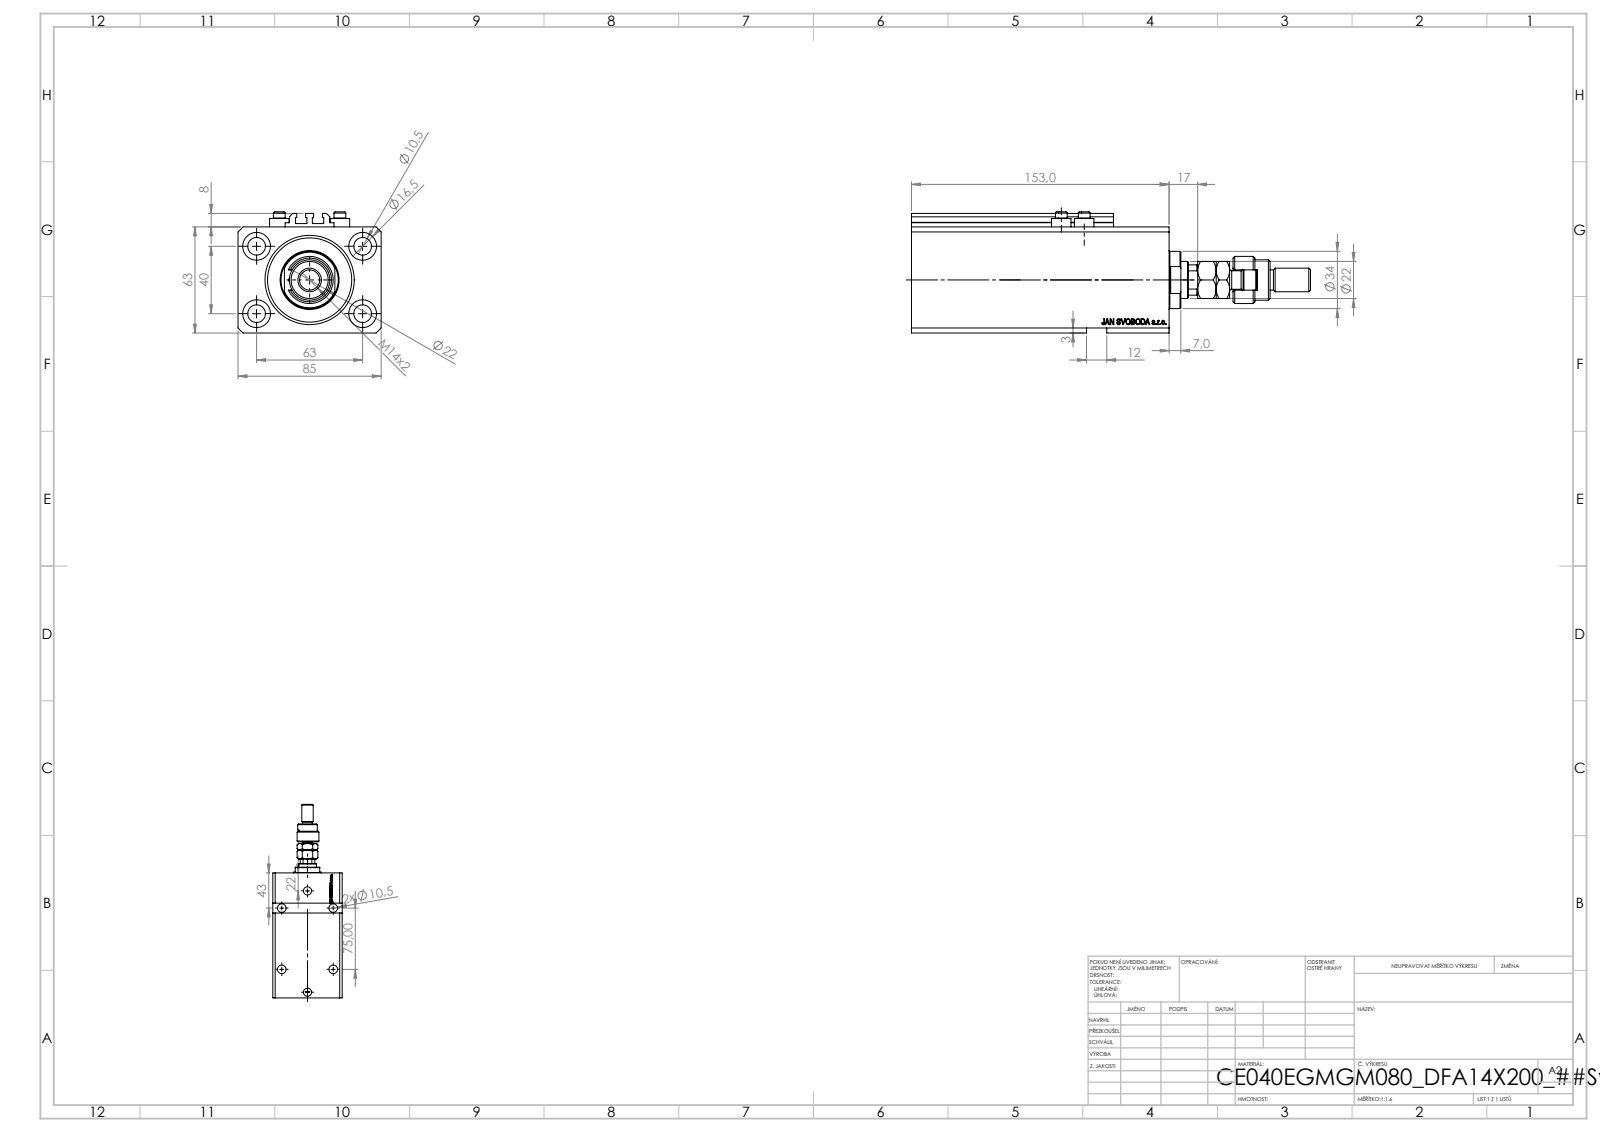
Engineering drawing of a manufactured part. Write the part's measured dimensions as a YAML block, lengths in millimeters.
part_name: "V250CE_C_VCP; FEMALE_PART_FOR_DFA; V250CE_VC_E; ALLEN BOLT V250CE (+2 more)"
step_written_by: "SolidWorks 2019 (CONFIG_CONTROL_DESIGN)"
units: millimeters
bodies: {solids: 10, faces: 1192, planar: 563, cylindrical: 159, other: 470}
overall_size: [237, 85, 72]
volume: 705763
surface_area: 148784
round_holes:
  - {diameter: 10.5, count: 8}
  - {diameter: 1.25, count: 4}
  - {diameter: 4, count: 4}
  - {diameter: 16.5, count: 4}
  - {diameter: 10, count: 2}
  - {diameter: 13.16, count: 2}
  - {diameter: 20, count: 2}
  - {diameter: 12.5, count: 1}
  - {diameter: 22, count: 1}
  - {diameter: 40, count: 1}
  - {diameter: 53, count: 1}
round_bosses_or_shafts:
  - {diameter: 11.6, count: 4}
  - {diameter: 7, count: 4}
  - {diameter: 34, count: 1}
  - {diameter: 28, count: 1}
  - {diameter: 24, count: 1}
  - {diameter: 18, count: 1}
  - {diameter: 14, count: 1}
  - {diameter: 12, count: 1}
partial_cylinders:
  - {radius: 0.2, count: 10}
  - {radius: 9.75, count: 1}
  - {radius: 10.5, count: 1}
face_to_face_distances: [63, 85, 17, 153, 136, 11.4, 124.6, 141.6, 3, 65]
hole_center_spacings: [37.31, 63, 13.6, 15.4, 24.96, 33.62, 36, 37.86]
